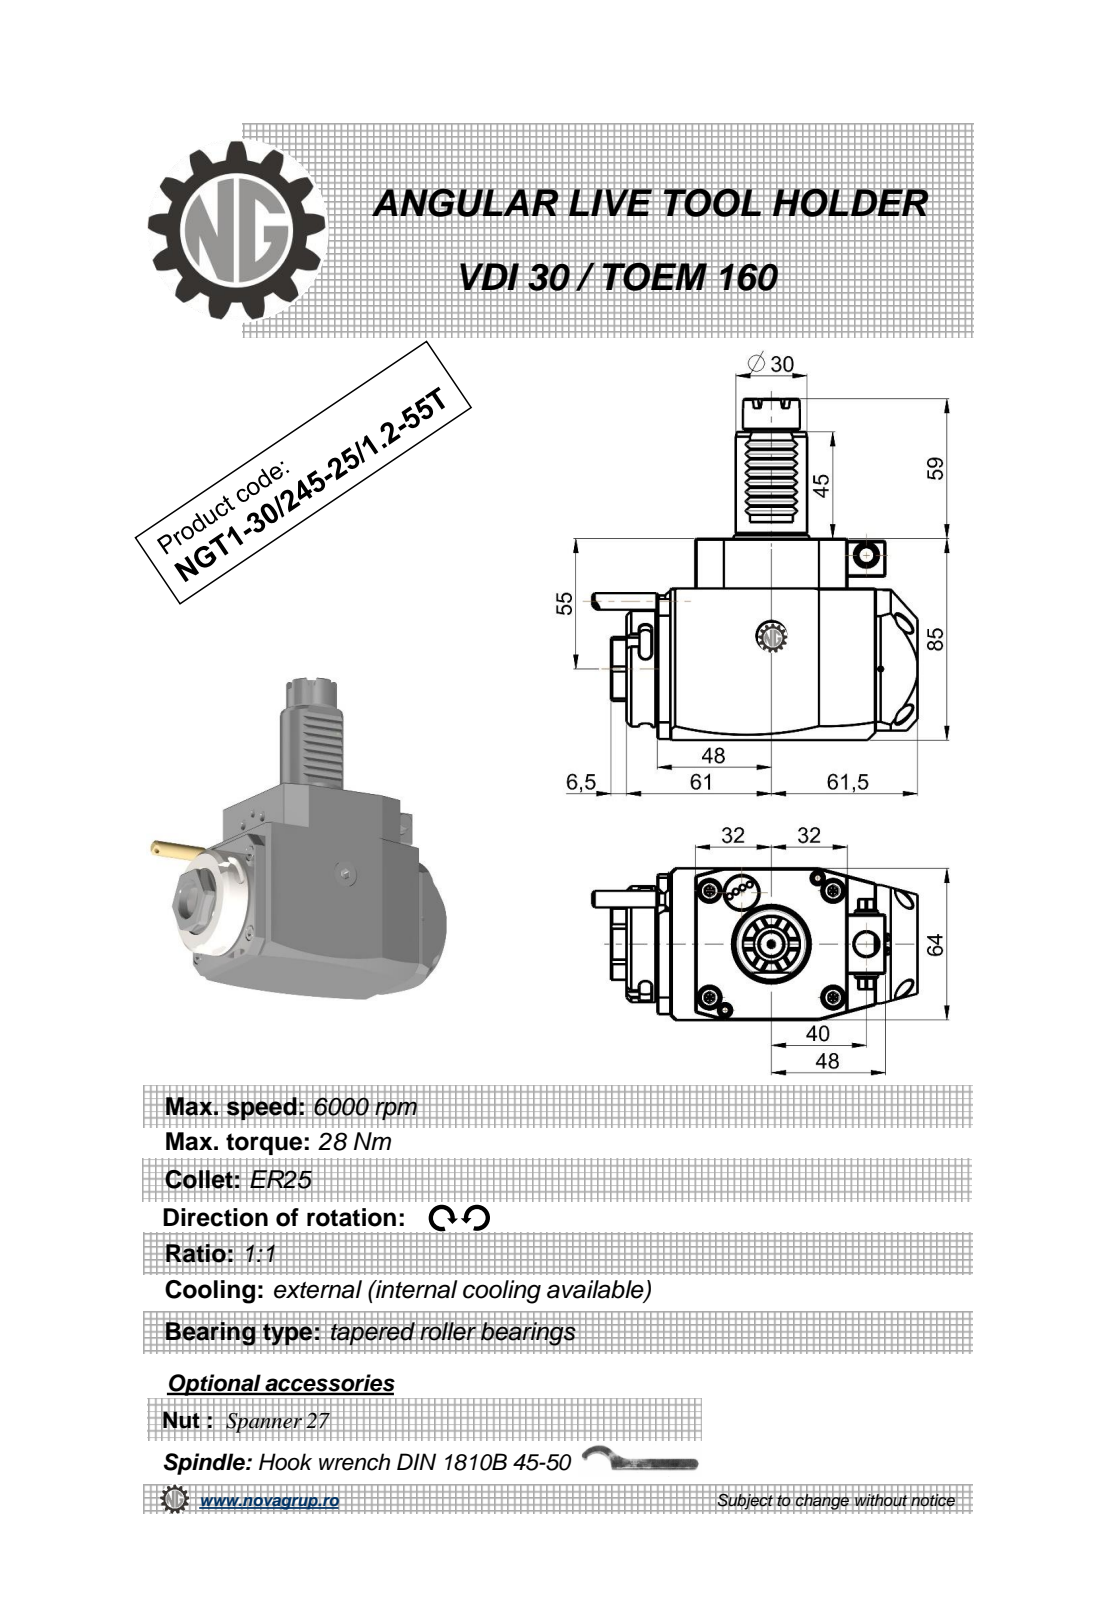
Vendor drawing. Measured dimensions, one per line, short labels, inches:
name: NGT1_30_245_25_1_2_55T
written by: PRO/ENGINEER BY PARAMETRIC TECHNOLOGY CORPORATION, 2010280 (CONFIG_CONTROL_DESIGN)
unit: in
bodies: 1 solid, 374 faces (210 planar, 82 cylindrical, 82 other)
size: 5.669 × 5.389 × 2.52
volume: 33.71 in³; area: 77.72 in²
holes: 1× ⌀0.098, 1× ⌀0.118, 1× ⌀0.335, 1× ⌀0.374, 1× ⌀0.394, 1× ⌀0.709
bosses: 2× ⌀0.315, 1× ⌀1.929, 1× ⌀1.654, 1× ⌀1.181, 1× ⌀0.945, 1× ⌀0.697, 1× ⌀0.598, 1× ⌀0.394
rounds: 8× R0.012, 6× R0.098, 2× R7.087, 1× R0.152, 1× R0.177, 1× R0.591, 1× R0.846, 1× R1.319
face distances: 2.52, 3.346, 0.63, 3.15, 0.512, 4.311, 0.827, 4.823, 1.142, 3.681
hole spacings: 1.03, 1.348, 1.831
